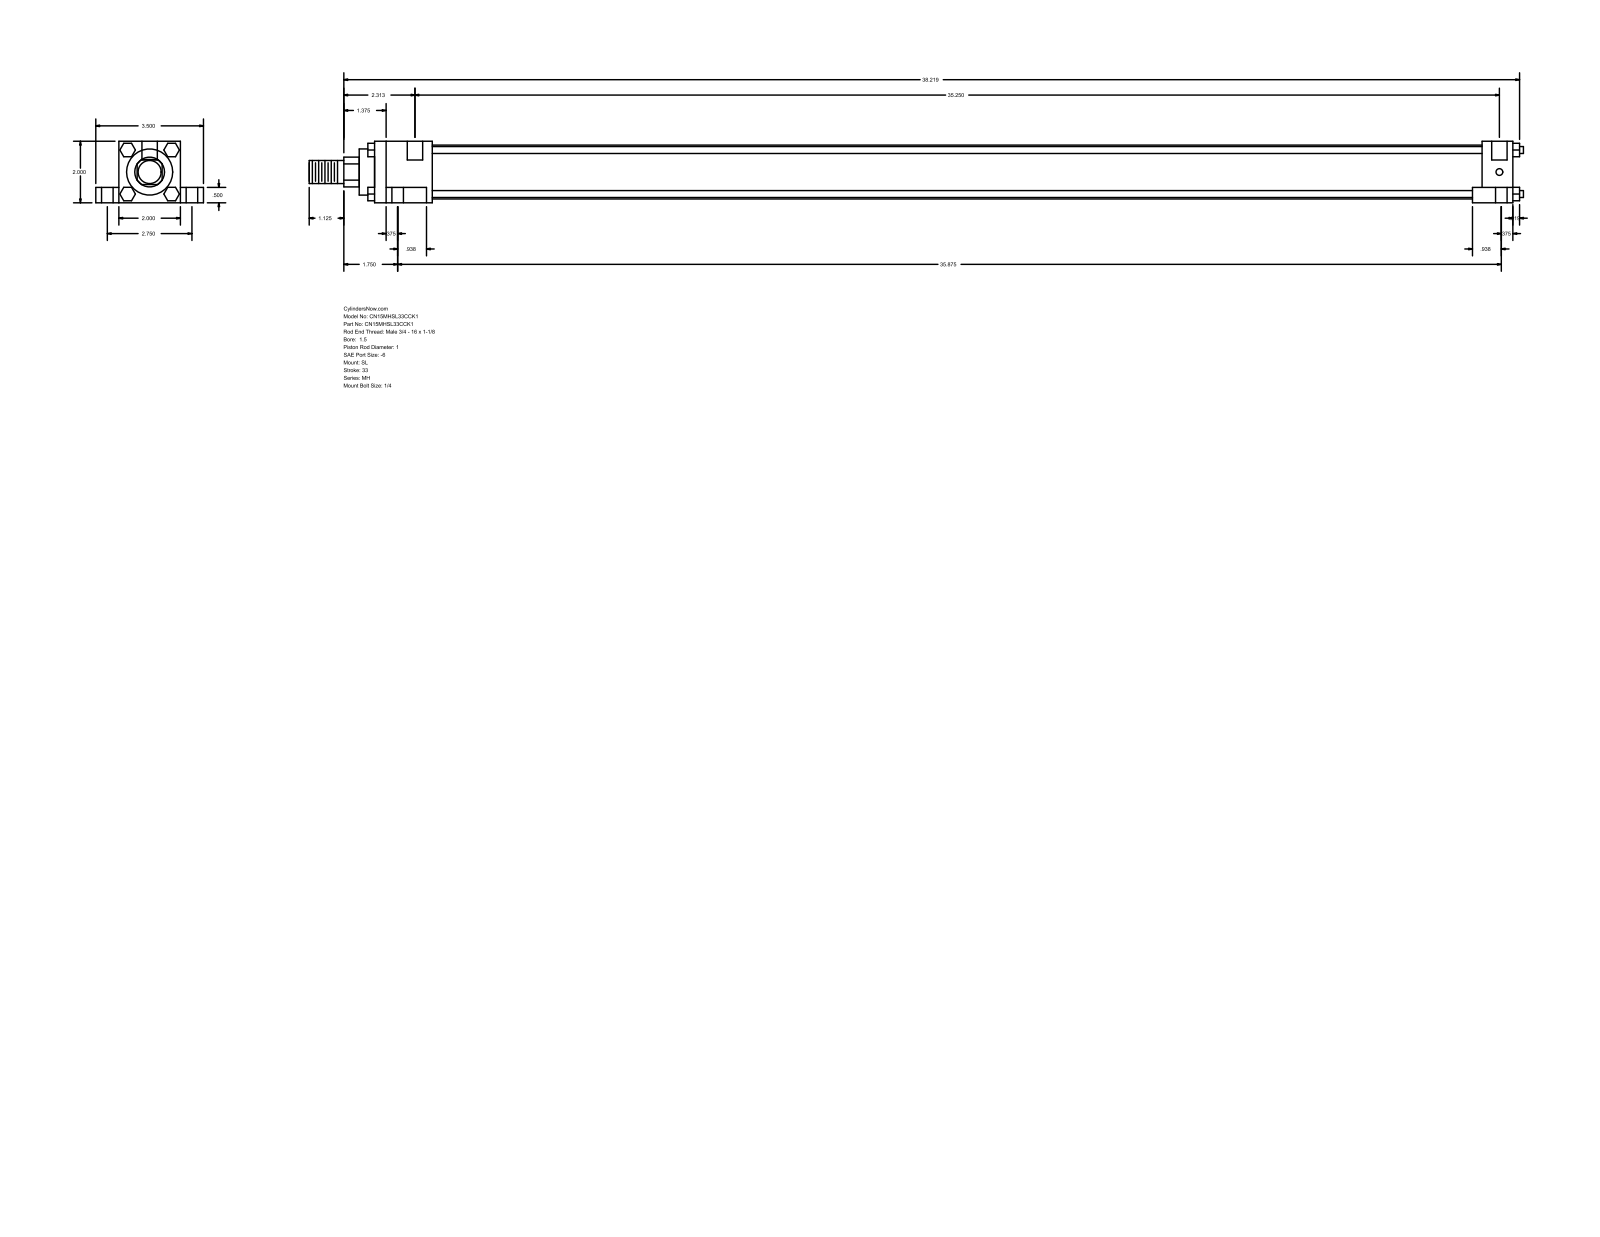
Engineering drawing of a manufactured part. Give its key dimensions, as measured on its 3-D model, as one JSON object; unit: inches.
{"part_name": "MH_SL__0150_1", "step_written_by": "GSSL Pune (CONFIG_CONTROL_DESIGN)", "units": "inches", "bodies": {"solids": 0, "faces": 148, "planar": 112, "cylindrical": 36, "other": 0}, "overall_size": [39.469, 3.5, 2], "round_holes": [[0.219, 4], [0.375, 4], [0.625, 4], [0.5, 2]], "round_bosses_or_shafts": [[0.225, 4], [1.75, 1], [1.5, 1], [1, 1], [0.75, 1]], "partial_cylinders_radius": [[0.484, 1]], "face_to_face_distances": [2, 0.5, 1.5, 0.75, 2.75, 37, 1, 0.375, 1.313, 35.313], "hole_center_spacings": [1.376, 1.443, 1.485, 2.75, 35.339, 35.375, 35.464, 35.839]}
